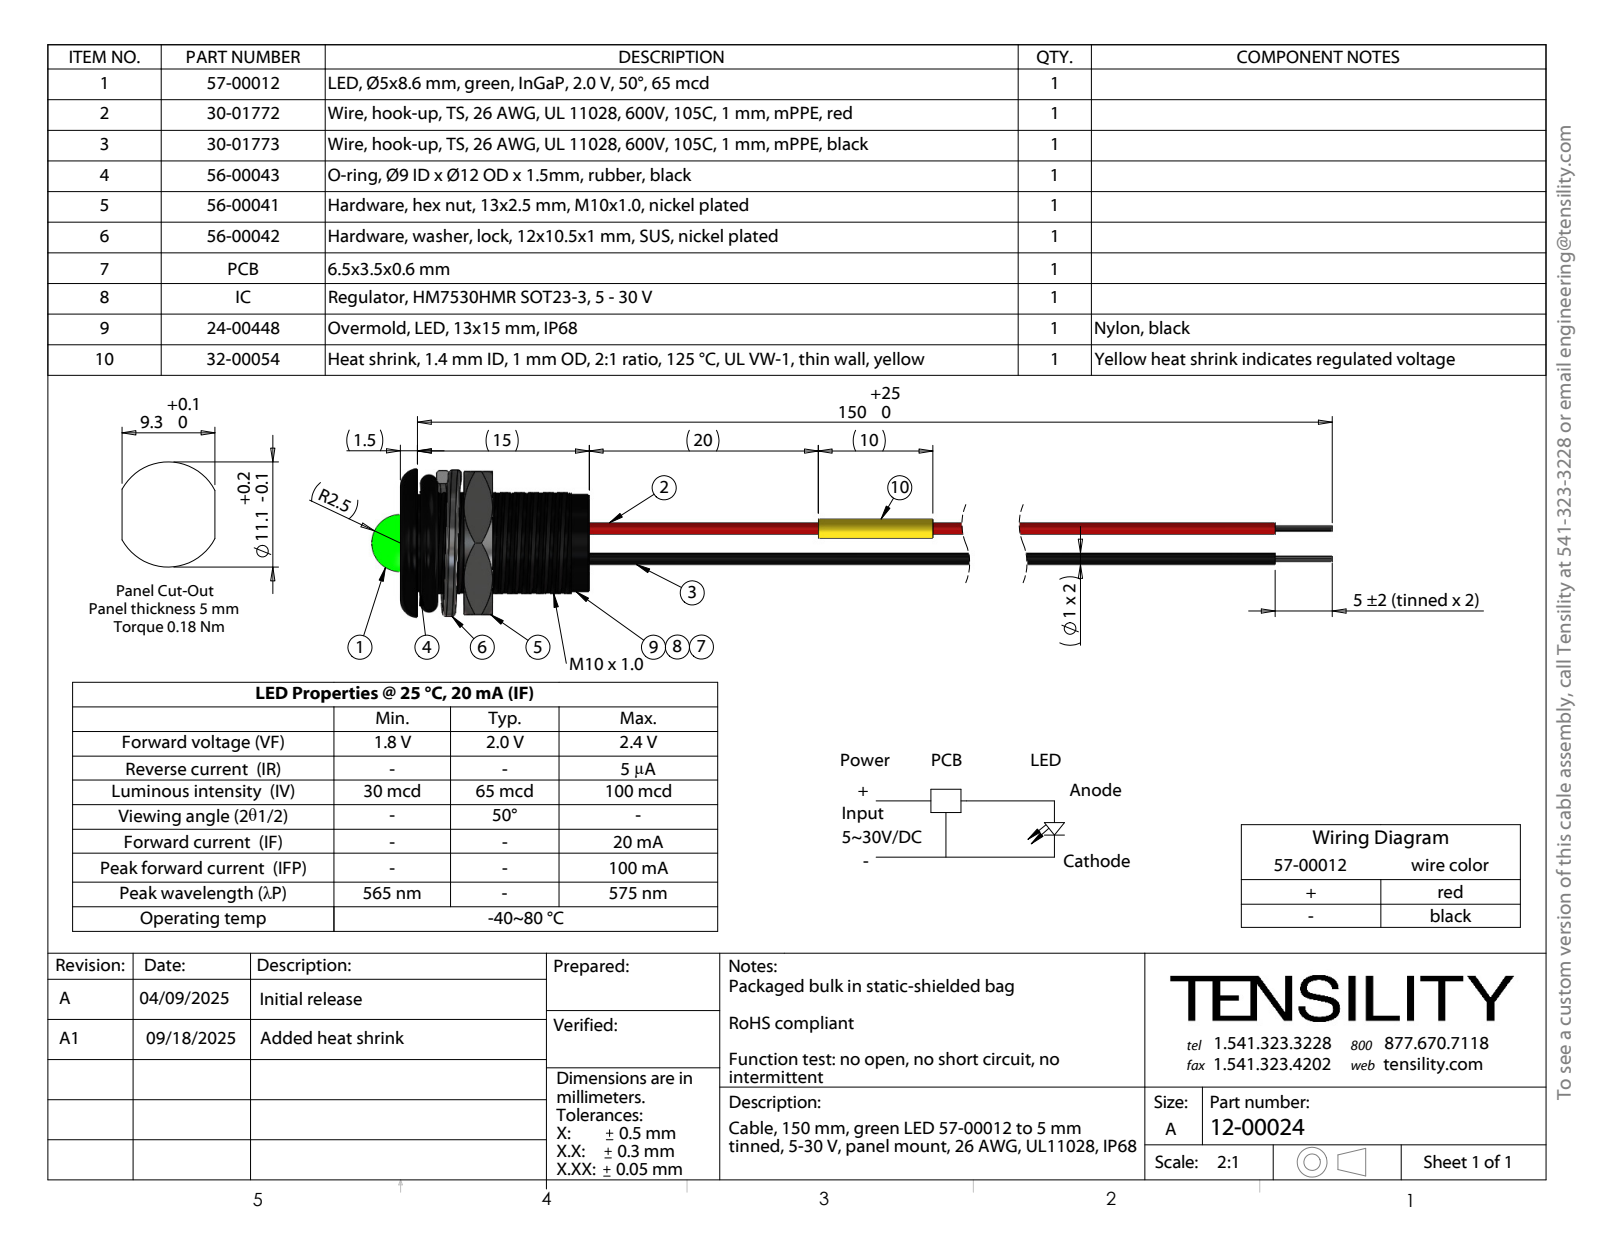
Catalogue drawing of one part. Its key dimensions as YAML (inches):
part_name: "56-00043; 30-01772_stripped and tinned; 24-00448; 56-00042_Split washer (+4 more)"
step_written_by: "SolidWorks 2021 (CONFIG_CONTROL_DESIGN)"
units: inches
bodies: {solids: 57, faces: 514, planar: 185, cylindrical: 246, other: 83}
overall_size: [6.85, 0.568, 0.511]
volume: 0.108
surface_area: 10.18
round_holes:
  - {diameter: 0.039, count: 2}
round_bosses_or_shafts:
  - {diameter: 0.039, count: 2}
  - {diameter: 0.033, count: 2}
  - {diameter: 0.335, count: 1}
  - {diameter: 0.197, count: 1}
partial_cylinders:
  - {radius: 0.17, count: 1}
  - {radius: 0.197, count: 1}
face_to_face_distances: [0.059, 0.65, 0.591, 0.492, 0.317, 0.258, 0.332, 0.219, 0.16, 0.098]
hole_center_spacings: [0.014, 0.015, 0.013, 0.096, 0.093, 0.098, 0.099, 0.101]
